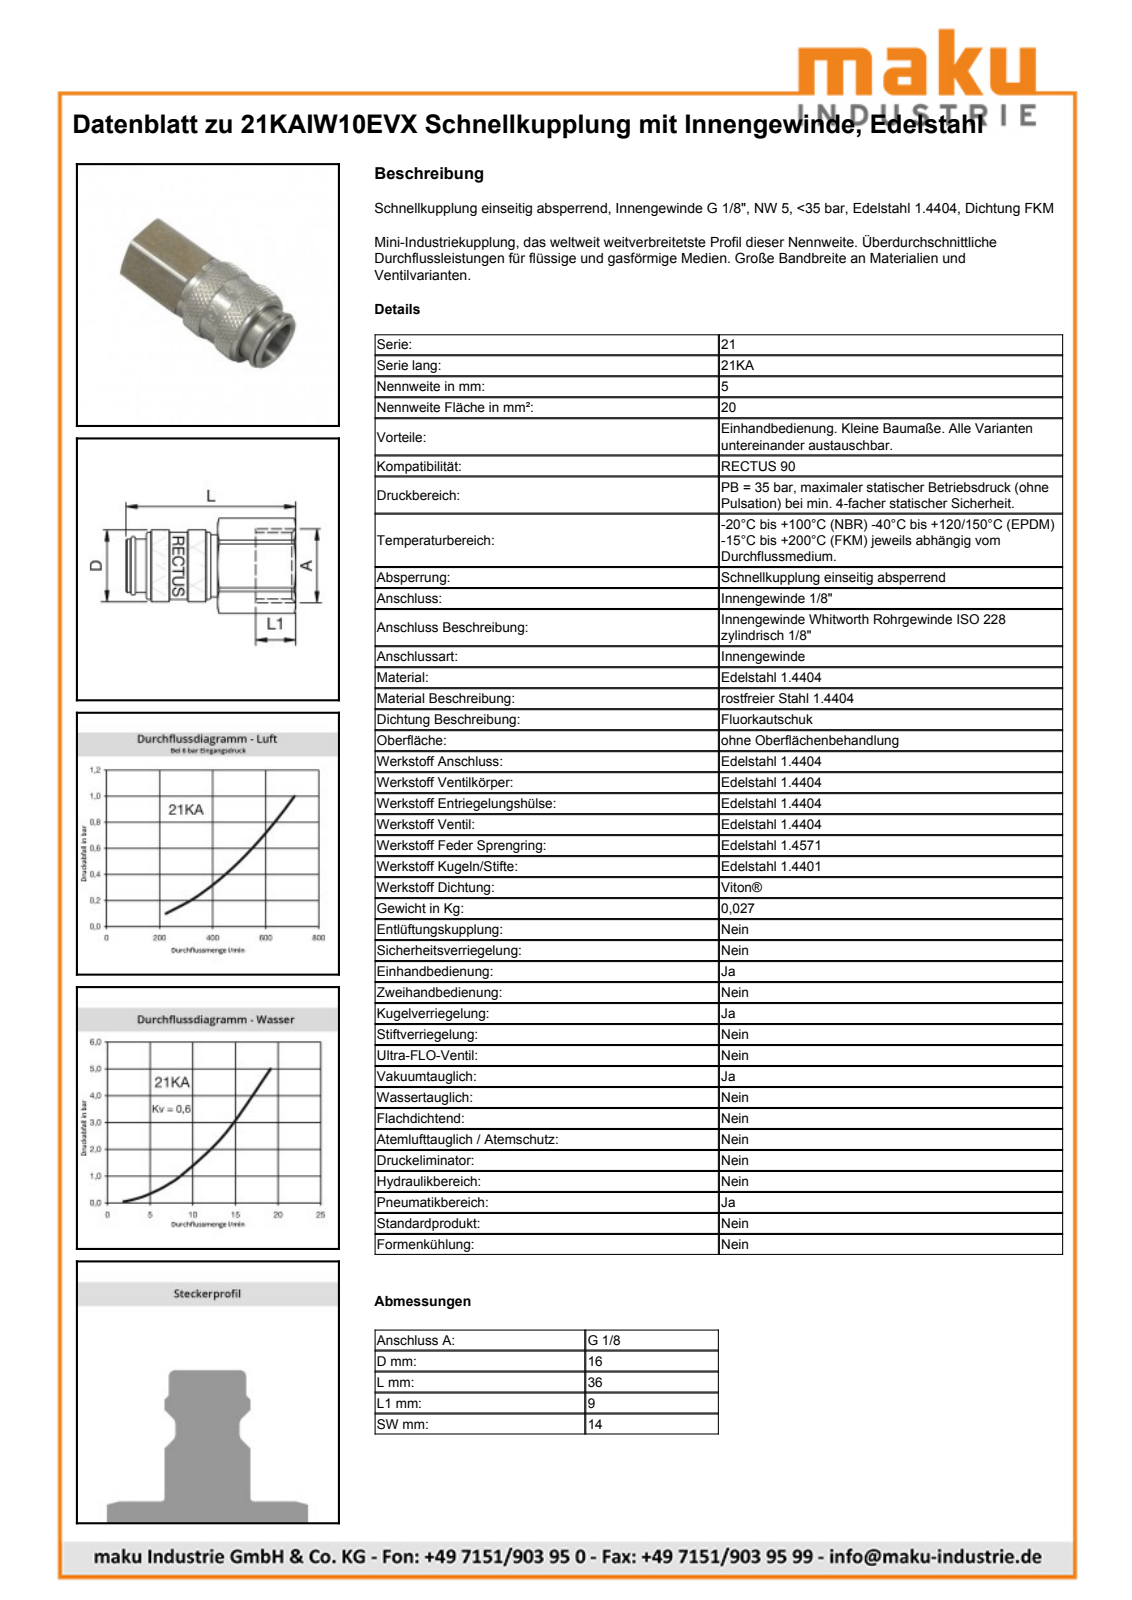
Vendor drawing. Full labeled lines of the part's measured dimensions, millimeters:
Part name (STEP PRODUCT): D110768
STEP written by: Autodesk Inventor 2013 (AUTOMOTIVE_DESIGN)
Units: millimetres
Bodies: 2 solids, 392 faces (163 planar, 63 cylindrical, 166 other)
Overall size (bounding box): 36.15 × 16.15 × 16.15
Volume: 5 343 mm³ · Surface area: 3 804 mm²
Round holes (diameter × count): ⌀8.57 ×1, ⌀12.15 ×1, ⌀14 ×1
Round bosses / shafts (diameter × count): ⌀16.15 ×1, ⌀15.1 ×1, ⌀12 ×1, ⌀11.4 ×1, ⌀11.15 ×1
Partial cylindrical surfaces — rounded edges, fillets, slot ends (radius × count): R5.55 ×1, R7.45 ×1, R7.9 ×1
Main face-to-face distances: 14, 27.15, 9, 36.15, 22.59, 4.56, 31.59, 11.86, 7.3, 15.29
